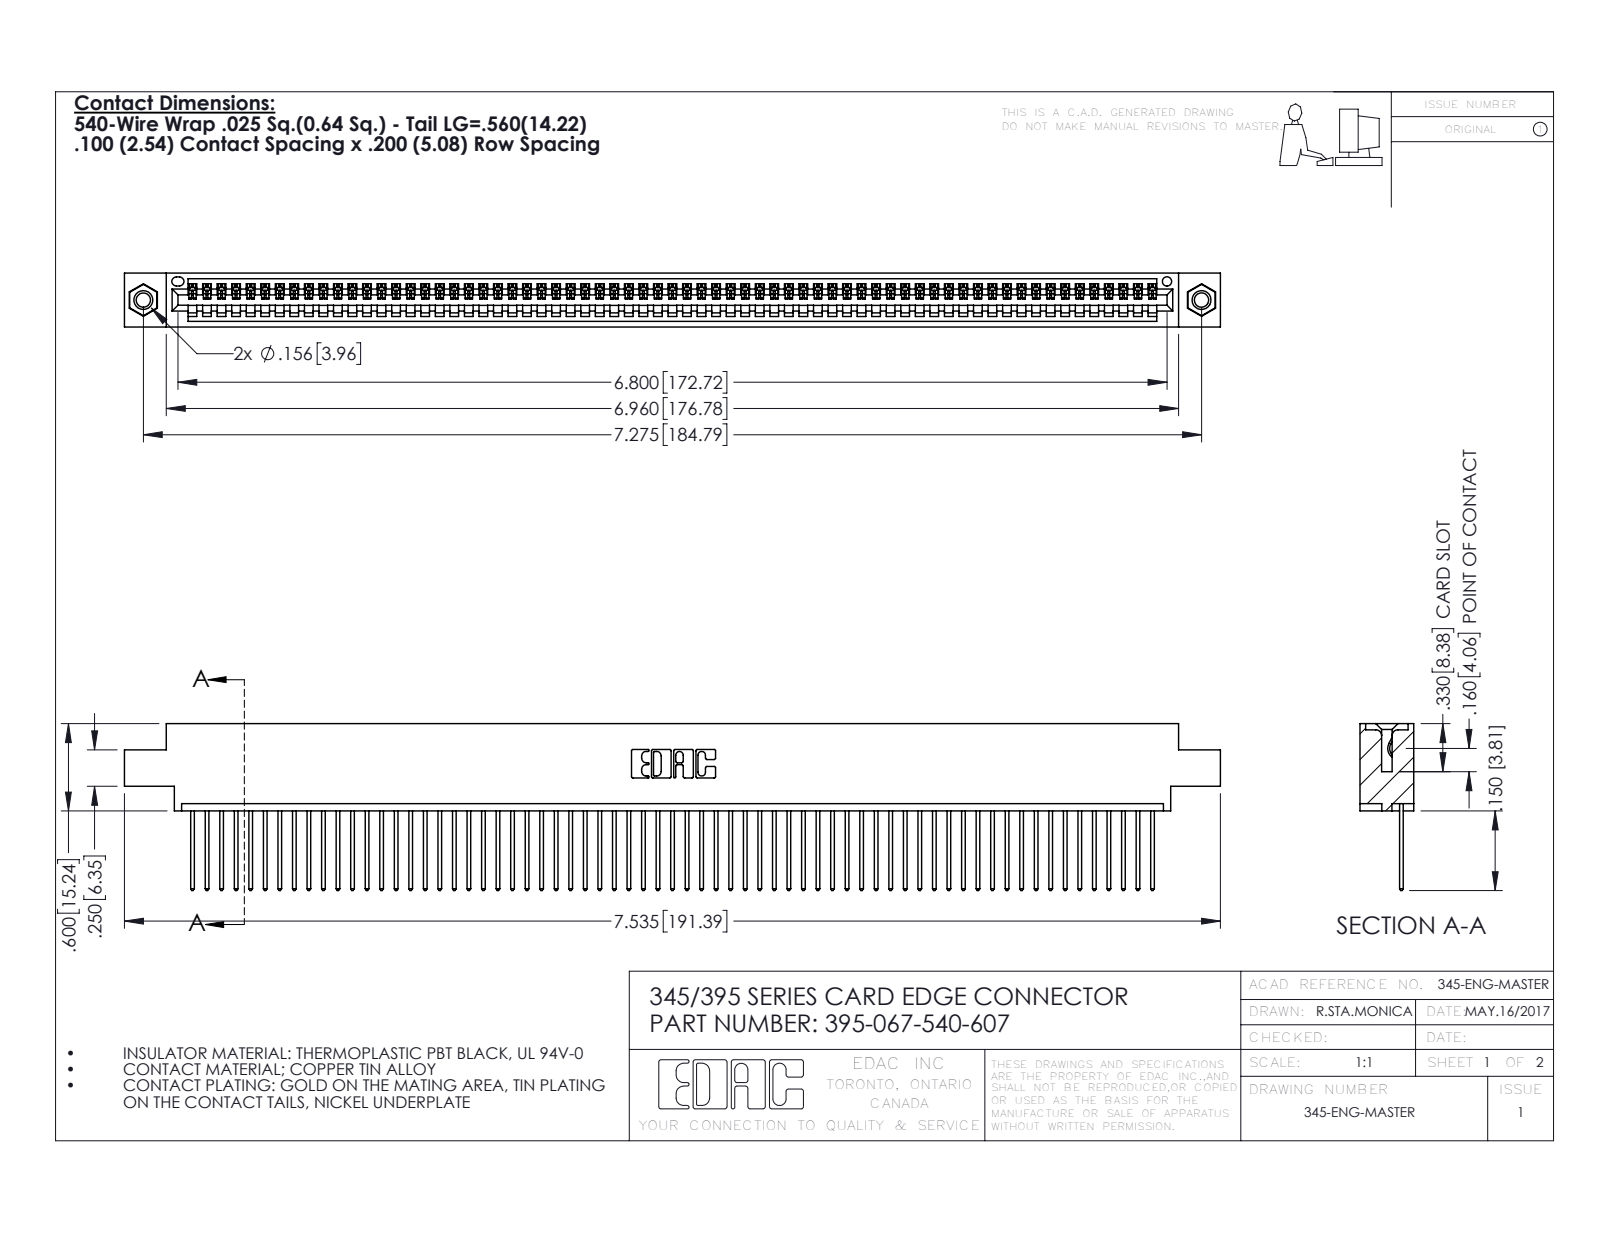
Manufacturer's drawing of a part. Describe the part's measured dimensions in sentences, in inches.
The part is named "395-067-540-607; 345-292-001_345-293-140; 345 Part_0.170 Offset - 0.156 Dia-TI; 345-250-001_345-250-005-103". Its 3-D file was written by "SolidWorks 2016 (CONFIG_CONTROL_DESIGN)". It is 70 solids with 4076 faces: 2796 planar, 1264 cylindrical and 16 other. Overall it measures 7.535 by 1.147 by 0.37 inches. Its volume is 1.12 cubic inches and its surface area 39.58 square inches. Round holes: 2 of diameter 0.098, 2 of diameter 0.125, 2 of diameter 0.156, 1 of diameter 0.064. Round bosses or shafts: 2 of diameter 0.155. Partial cylindrical surfaces (rounded edges, fillets, slot ends): 134 of radius 0.006, 134 of radius 0.01, 22 of radius 0.01, 6 of radius 0.007, 6 of radius 0.031, 3 of radius 0.026, 2 of radius 0.031, 2 of radius 0.04. The main face-to-face distances are 0.072, 0.298, 0.37, 0.098, 0.272, 0.025, 0.2, 0.225, 0.175, 0.149. The hole center spacings are 0.27, 7.039, 7.275.
